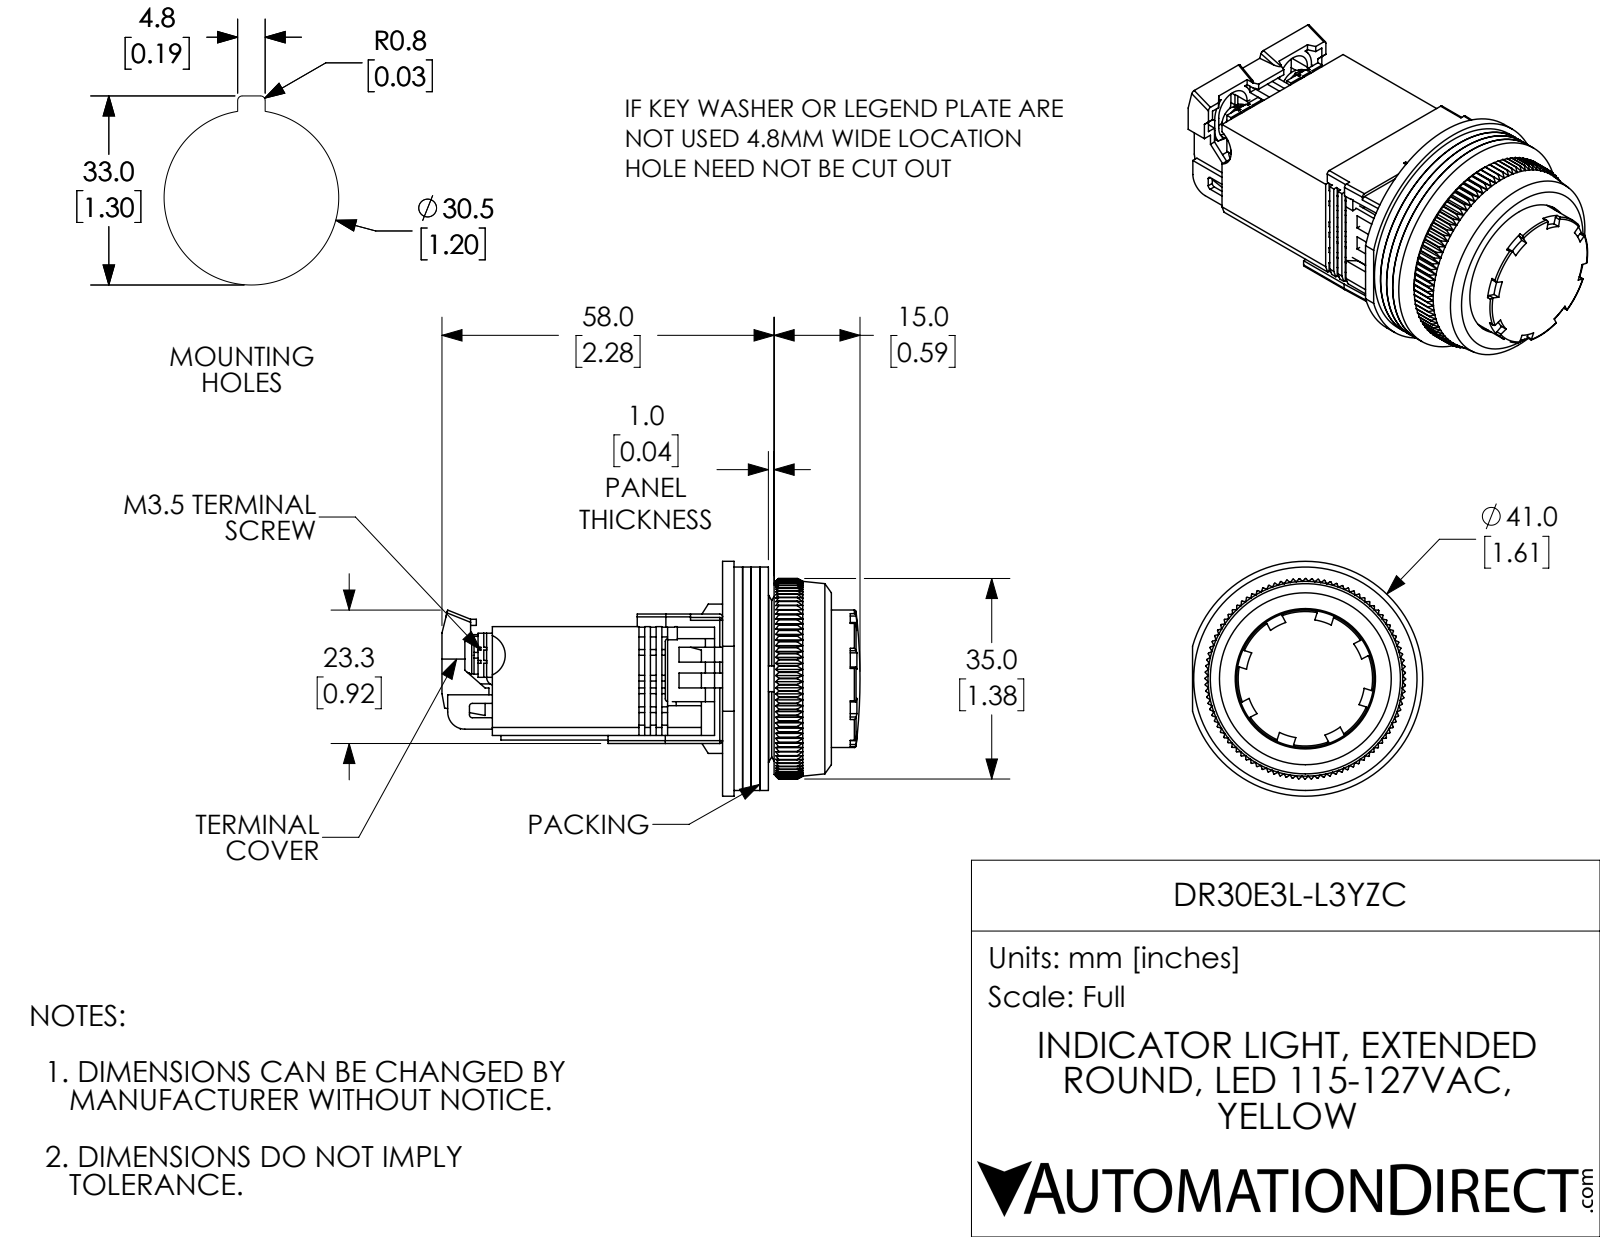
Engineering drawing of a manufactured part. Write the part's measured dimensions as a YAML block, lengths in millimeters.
part_name: "DR30B5-EBZC"
step_written_by: "SolidWorks 2017 (AUTOMOTIVE_DESIGN)"
units: millimeters
bodies: {solids: 18, faces: 1273, planar: 854, cylindrical: 315, other: 104}
overall_size: [64.5, 44, 41]
volume: 34150
surface_area: 31140
round_holes:
  - {diameter: 2.5, count: 3}
  - {diameter: 3.5, count: 3}
  - {diameter: 3, count: 2}
  - {diameter: 3.6, count: 2}
  - {diameter: 4, count: 1}
  - {diameter: 18, count: 1}
  - {diameter: 22, count: 1}
  - {diameter: 28.3, count: 1}
  - {diameter: 29.8, count: 1}
round_bosses_or_shafts:
  - {diameter: 6.6, count: 2}
  - {diameter: 3.5, count: 2}
  - {diameter: 41, count: 1}
  - {diameter: 39, count: 1}
  - {diameter: 30, count: 1}
  - {diameter: 30, count: 1}
  - {diameter: 28, count: 1}
  - {diameter: 21, count: 1}
partial_cylinders:
  - {radius: 0.5, count: 31}
  - {radius: 1, count: 12}
  - {radius: 1.5, count: 8}
  - {radius: 3, count: 2}
  - {radius: 0.7, count: 1}
  - {radius: 1.6, count: 1}
  - {radius: 1.7, count: 1}
  - {radius: 4, count: 1}
face_to_face_distances: [1.5, 3, 1, 4.5, 17.5, 2, 9, 14.5, 13, 18.5]
hole_center_spacings: [4.5, 6.4, 9, 12, 12.8, 12.9, 15, 16.5]
